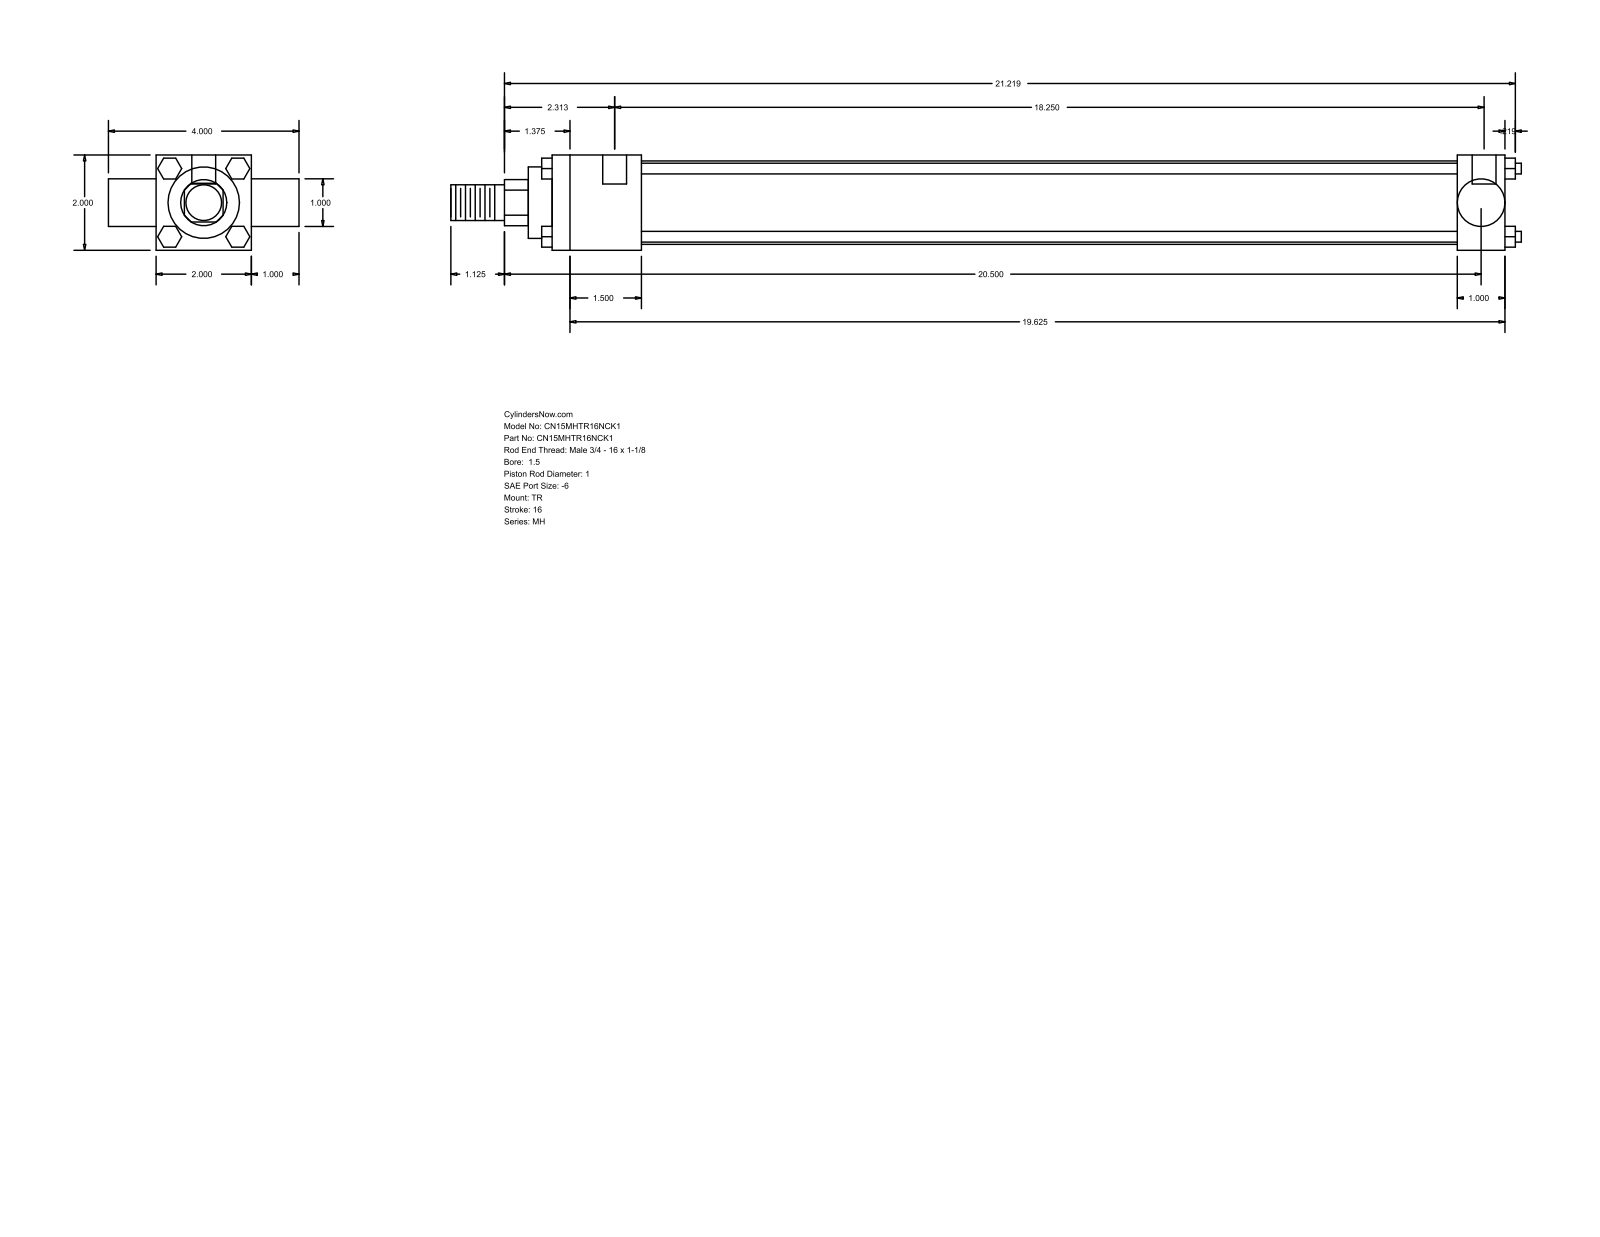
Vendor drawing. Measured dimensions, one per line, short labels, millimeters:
name: MH_TR__0150_1
written by: GSSL Pune (CONFIG_CONTROL_DESIGN)
unit: mm
bodies: 0 solids, 120 faces (92 planar, 28 cylindrical, 0 other)
size: 570.71 × 101.6 × 50.8
holes: 3× ⌀5.56, 2× ⌀12.7
bosses: 4× ⌀5.71, 1× ⌀44.45, 1× ⌀38.1, 1× ⌀25.4, 1× ⌀25.35, 1× ⌀19.05
rounds: 1× R12.29
face distances: 50.8, 25.4, 508, 76.2, 47.63, 460.37, 482.6, 434.97, 101.6, 12.7
hole spacings: 3.18, 463.55, 466.73
